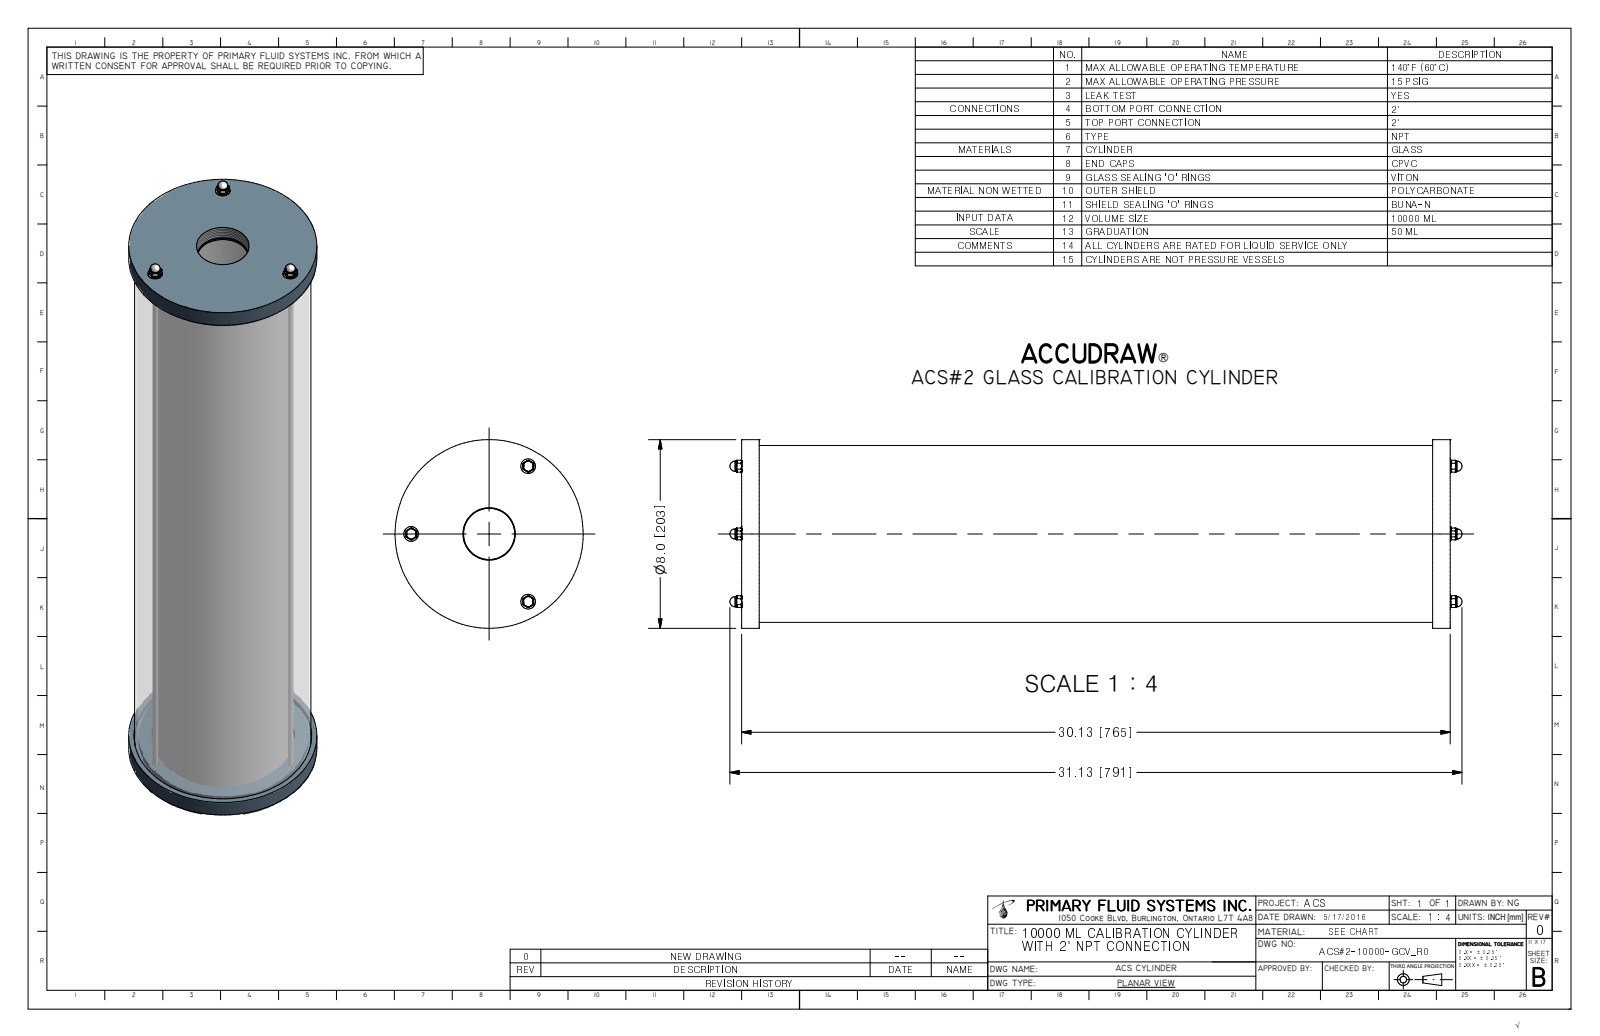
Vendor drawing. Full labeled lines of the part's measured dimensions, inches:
Part name (STEP PRODUCT): ACS#2-10000-GCV_R0; ACS-3-10000-POLY_R3; ACS-2-10000_R6; ACS-1-10000-A_R0 (+3 more)
STEP written by: Autodesk Inventor 2009 (AUTOMOTIVE_DESIGN)
Units: inches
Bodies: 19 solids, 429 faces (38 planar, 41 cylindrical, 350 other)
Overall size (bounding box): 31.128 × 8 × 8
Volume: 253.4 in³ · Surface area: 2 772 in²
Round holes (diameter × count): ⌀0.18 ×3, ⌀0.266 ×3, ⌀0.281 ×3, ⌀5.512 ×1, ⌀6.068 ×1, ⌀7.25 ×1, ⌀7.55 ×1
Round bosses / shafts (diameter × count): ⌀0.625 ×3, ⌀0.25 ×3, ⌀8 ×1, ⌀7.5 ×1, ⌀7.2 ×1, ⌀5.906 ×1, ⌀5.427 ×1
Main face-to-face distances: 30.128, 0.75, 29.378, 28.628, 0.375, 29.753, 0.375, 29.003, 0.475, 29.653
Hole centre spacings: 3.317, 5.745, 5.745
